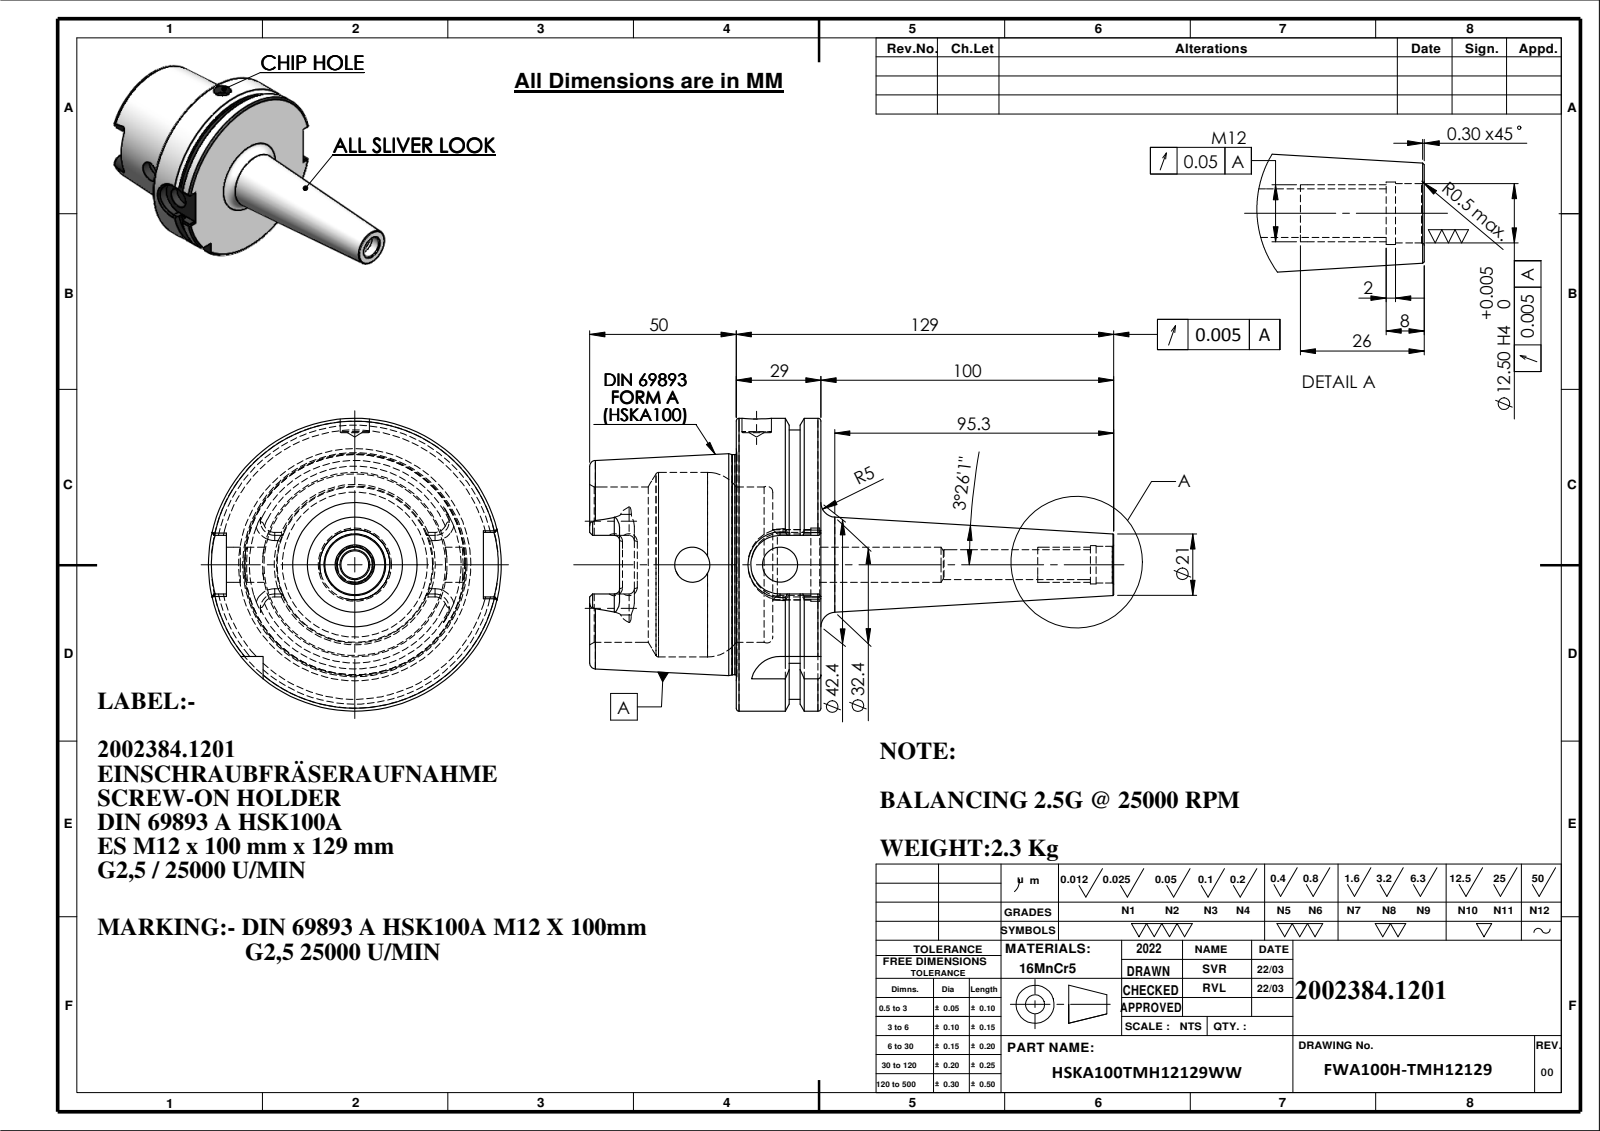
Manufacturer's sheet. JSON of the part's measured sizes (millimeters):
{"part_name": "91100A-ES8M12100", "step_written_by": "SolidWorks 2018 (CONFIG_CONTROL_DESIGN)", "units": "millimeters", "bodies": {"solids": 1, "faces": 176, "planar": 50, "cylindrical": 52, "other": 74}, "overall_size": [178.95, 100, 100], "volume_mm3": 302581, "surface_area_mm2": 61014, "round_holes": [[12, 3], [10, 1], [10.2, 1], [12.5, 1], [13.1, 1], [21, 1], [25, 1], [53, 1], [63, 1]], "round_bosses_or_shafts": [[100, 1], [92, 1], [75.16, 1]], "partial_cylinders_radius": [[1.8, 6], [4.88, 4], [10, 2], [11, 1]], "face_to_face_distances": [28.95, 12.5, 16.45, 50, 62.5, 78.95, 71.87, 21.87, 9.37, 7.08], "hole_center_spacings": [30]}
